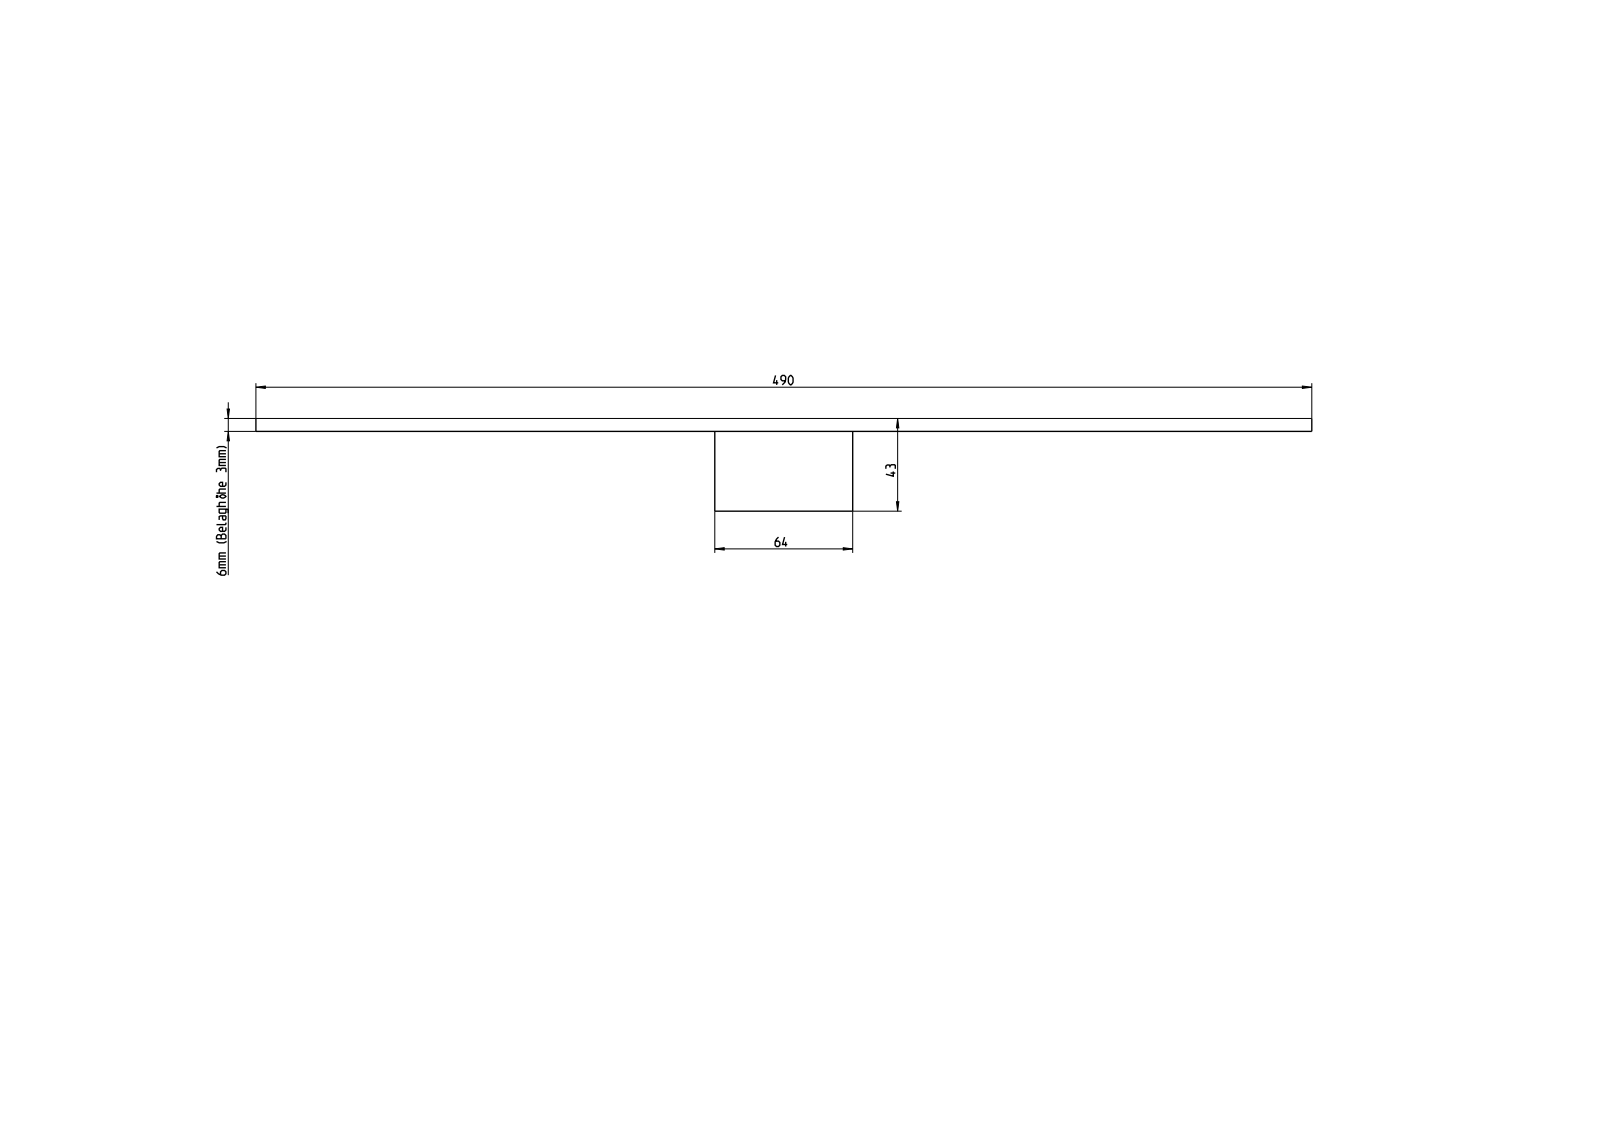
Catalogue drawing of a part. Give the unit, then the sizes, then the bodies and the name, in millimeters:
Units: millimetres
Overall size (bounding box): 499 × 490 × 43
Main face-to-face distances: 6, 37, 490, 499, 462, 43, 212.95, 276.95, 64, 277.05
Volume: 1 554 000 mm³ · Surface area: 509 946 mm²
Bodies: 2 solids, 16 faces (16 planar, 0 cylindrical, 0 other)
Part name (STEP PRODUCT): 1BKG5002W3LA; AUSLASS; BKG5002W3LA_ASM
STEP written by: CREO PARAMETRIC BY PTC INC, 2022024 (AUTOMOTIVE_DESIGN)
